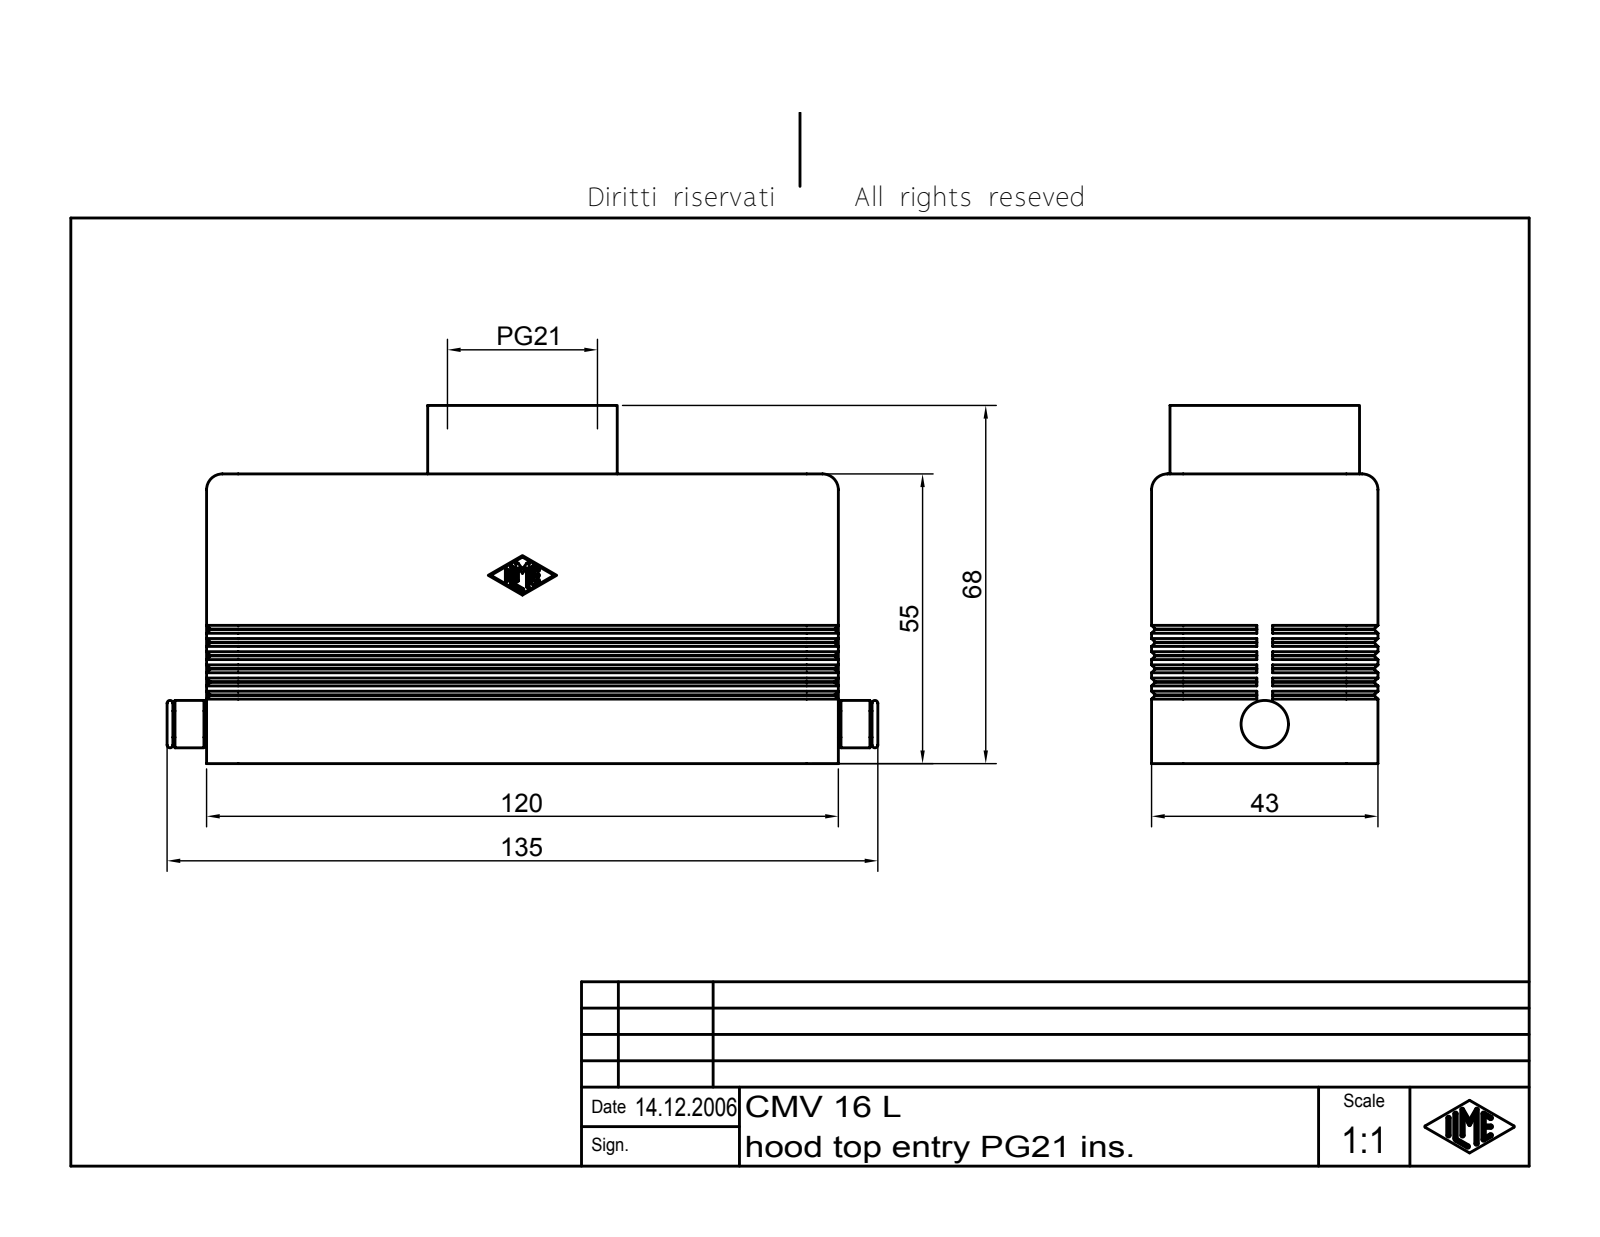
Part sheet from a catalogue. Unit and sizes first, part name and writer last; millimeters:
Units: millimetres
Overall size (bounding box): 135 × 68 × 43
Round holes (diameter × count): ⌀21.62 ×1, ⌀26.78 ×1
Round bosses / shafts (diameter × count): ⌀36 ×1, ⌀9 ×1, ⌀5 ×1
Partial cylindrical surfaces — rounded edges, fillets, slot ends (radius × count): R0.25 ×14, R3 ×8, R2 ×4, R6 ×4, R5.3 ×2, R1.5 ×1
Main face-to-face distances: 3, 40, 37, 43, 11.5, 8.5, 1.77, 117, 5.3, 120
Volume: 79 631 mm³ · Surface area: 47 343 mm²
Bodies: 1 solid, 496 faces (183 planar, 115 cylindrical, 198 other)
Part name (STEP PRODUCT): CH Tüllengehäuse für einen Einsatz Teil 4
STEP written by: Autodesk Inventor 7 (AUTOMOTIVE_DESIGN)
